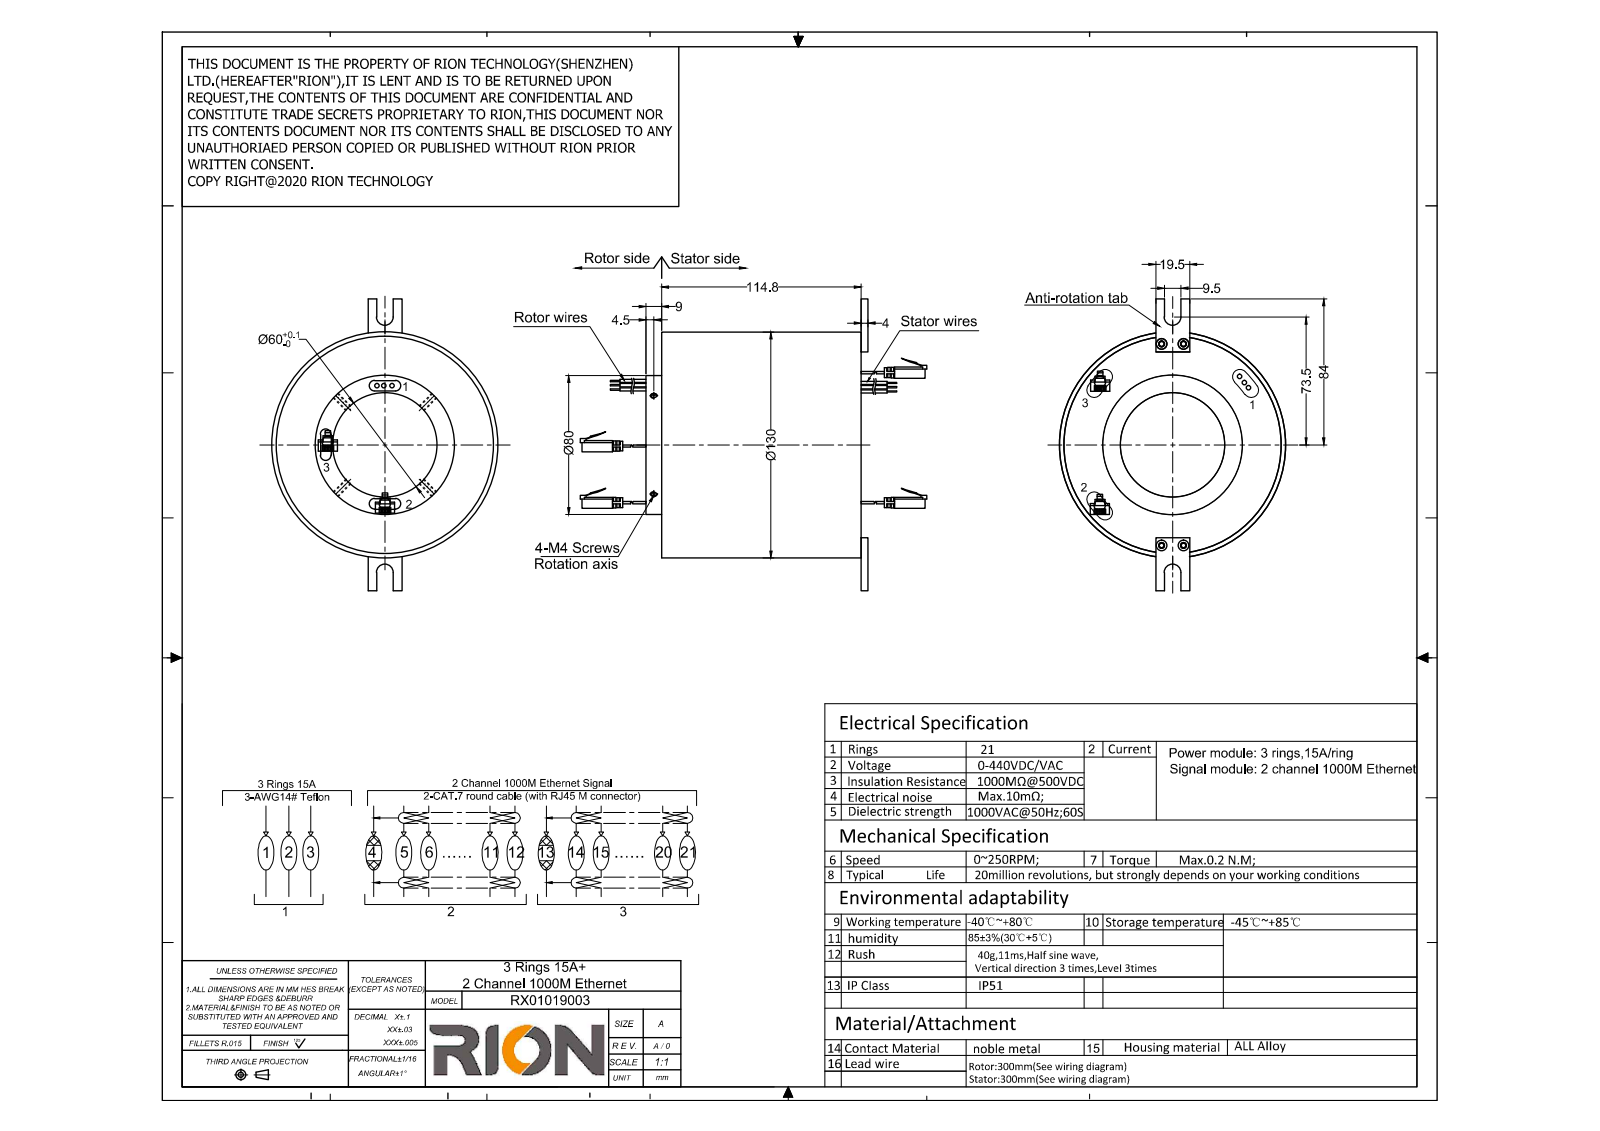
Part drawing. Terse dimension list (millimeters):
name: RX01019003
written by: SolidWorks 2014 (AUTOMOTIVE_DESIGN)
unit: mm
bodies: 1 solid, 165 faces (68 planar, 81 cylindrical, 16 other)
size: 181.8 × 168 × 130
volume: 1 226 000 mm³; area: 106 504 mm²
holes: 4× ⌀2.5, 4× ⌀3.2, 4× ⌀3.3, 1× ⌀60, 1× ⌀70, 1× ⌀125
bosses: 6× ⌀2.5, 4× ⌀6.5, 1× ⌀130, 1× ⌀124.8, 1× ⌀80, 1× ⌀69.8
rounds: 6× R2, 6× R4, 2× R4.75
face distances: 114.8, 9, 123.8, 4, 127.8, 118.8, 1, 122.8, 5, 113.8
hole spacings: 58.35, 12.7, 116, 116.69
